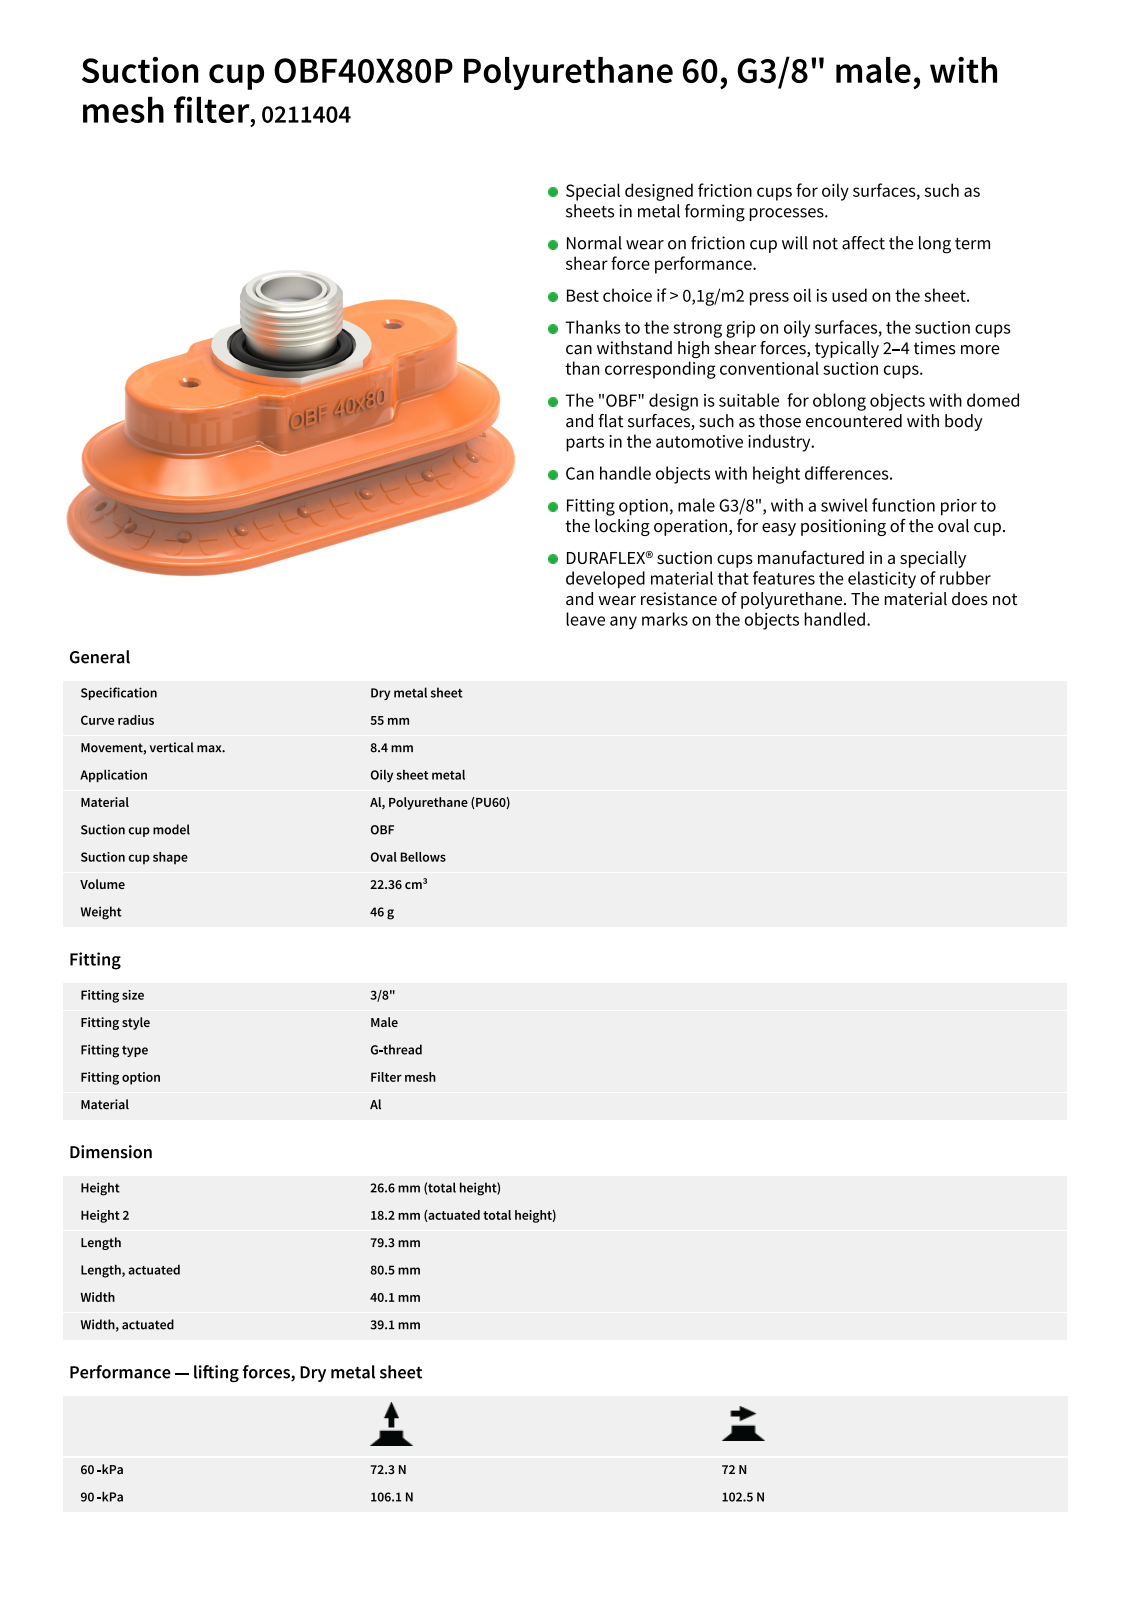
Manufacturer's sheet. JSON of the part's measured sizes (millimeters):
{"part_name": "SE-0419027; SE-0419029; 0107148; 0106793 (+4 more)", "step_written_by": "ST-DEVELOPER v16.7 (AUTOMOTIVE_DESIGN)", "units": "millimeters", "bodies": {"solids": 6, "faces": 412, "planar": 160, "cylindrical": 184, "other": 68}, "overall_size": [80, 40, 37], "volume_mm3": 50879, "surface_area_mm2": 16361, "round_holes": [[2, 8], [3, 2], [10, 1], [11.5, 1], [11.6, 1], [17, 1], [19, 1], [21, 1]], "round_bosses_or_shafts": [[16.66, 1], [14.8, 1], [11.3, 1]], "partial_cylinders_radius": [[1, 26], [2, 16], [0.5, 6], [1.52, 4], [1.56, 4], [2.81, 3], [0.9, 2], [1.08, 2]], "face_to_face_distances": [25.5, 7.5, 18, 2.5, 1.5, 3.5, 22, 5, 23.5, 4], "hole_center_spacings": [4, 5, 6.4, 10, 10.77, 16.76, 20.62, 36]}
